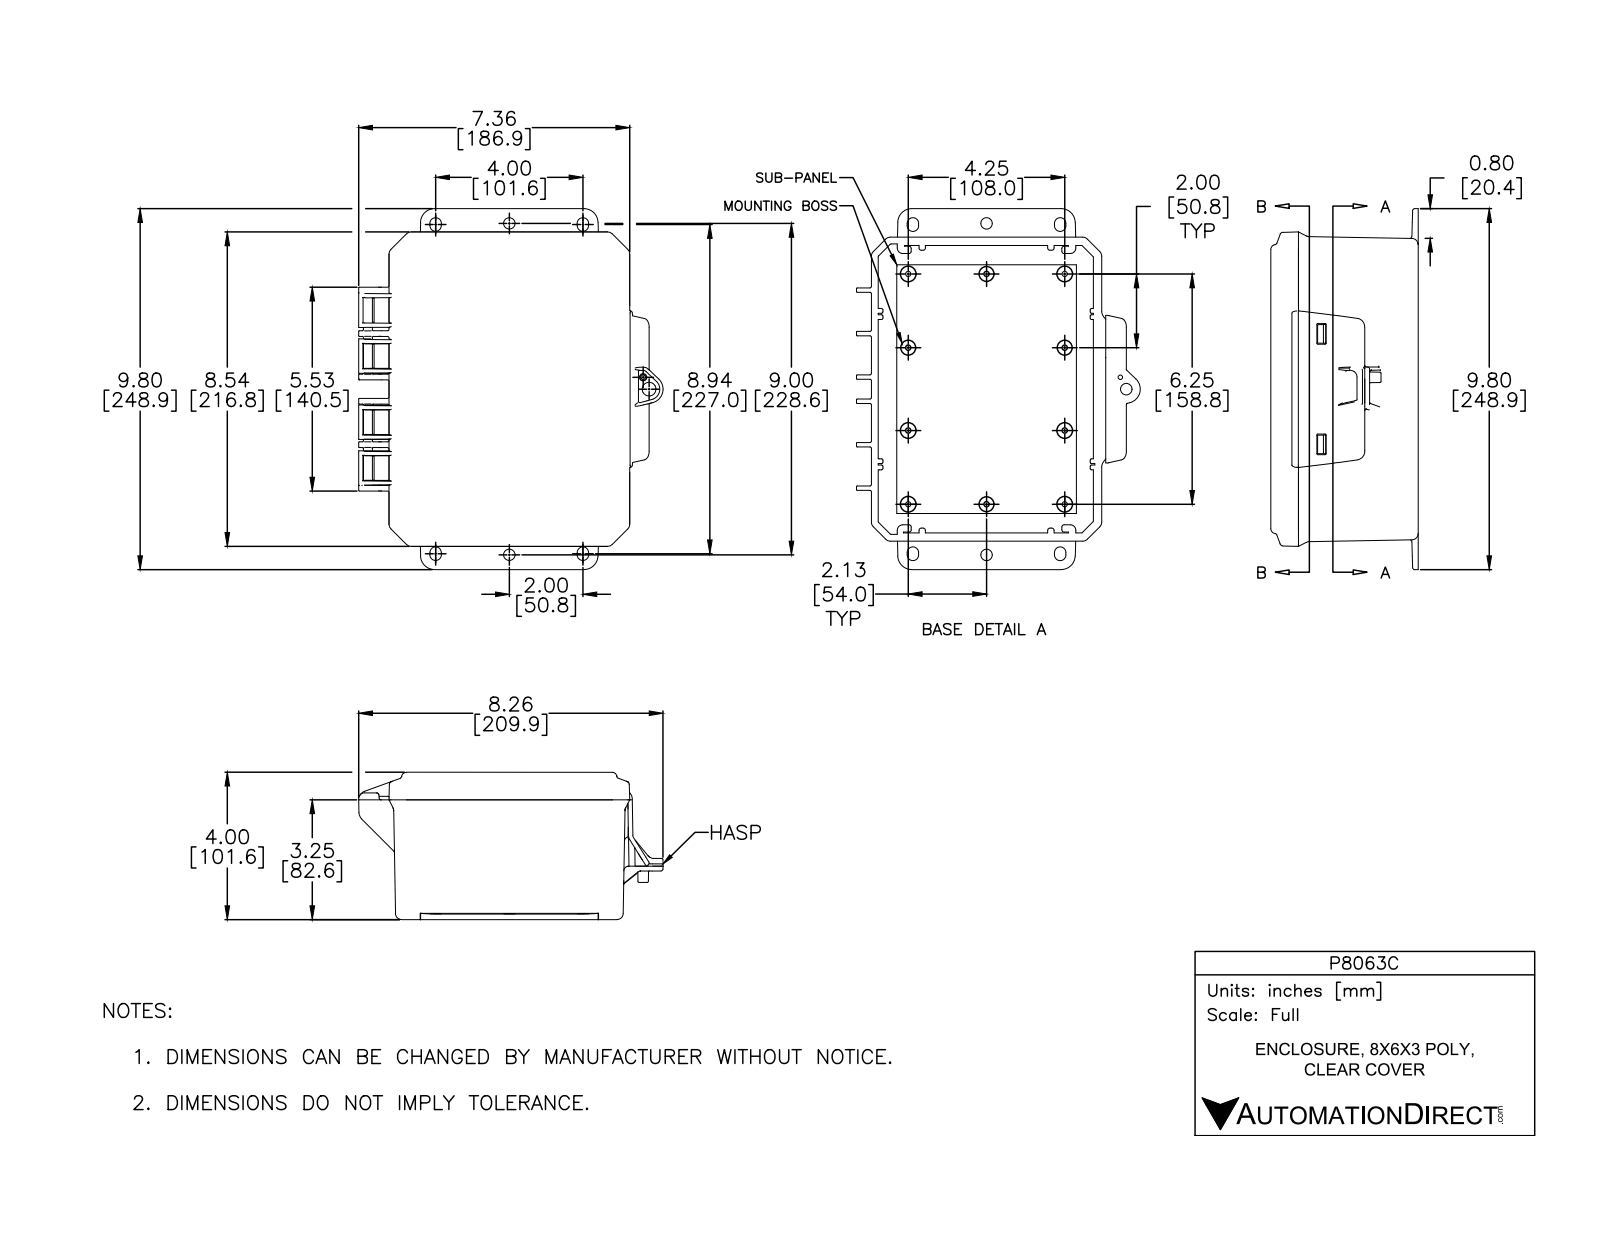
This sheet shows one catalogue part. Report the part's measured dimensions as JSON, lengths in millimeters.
{"part_name": "8X6X3-BOX-SD-HINGE-INT-LATCH_12; P8063C; 8X6-LID-SD-HINGE-INT-LATCH_126", "step_written_by": "SolidWorks 2016 (AUTOMOTIVE_DESIGN)", "units": "millimeters", "bodies": {"solids": 1, "faces": 2266, "planar": 571, "cylindrical": 841, "other": 854}, "overall_size": [248.9, 210, 101.7], "volume_mm3": 216600, "surface_area_mm2": 340400, "round_holes": [[3.6, 10], [3, 1]], "round_bosses_or_shafts": [[6.1, 1]], "partial_cylinders_radius": [[0.5, 124], [0.8, 117], [0.4, 63], [1, 54], [0.3, 33], [1.5, 32], [4.8, 17], [1.3, 15]], "face_to_face_distances": [3.8, 12, 9.5, 82.6, 78.7, 161.6, 157.8, 2.5, 3, 145.1], "hole_center_spacings": [50.8, 54, 74.1, 108, 108, 119.3, 120.7, 152.7]}
